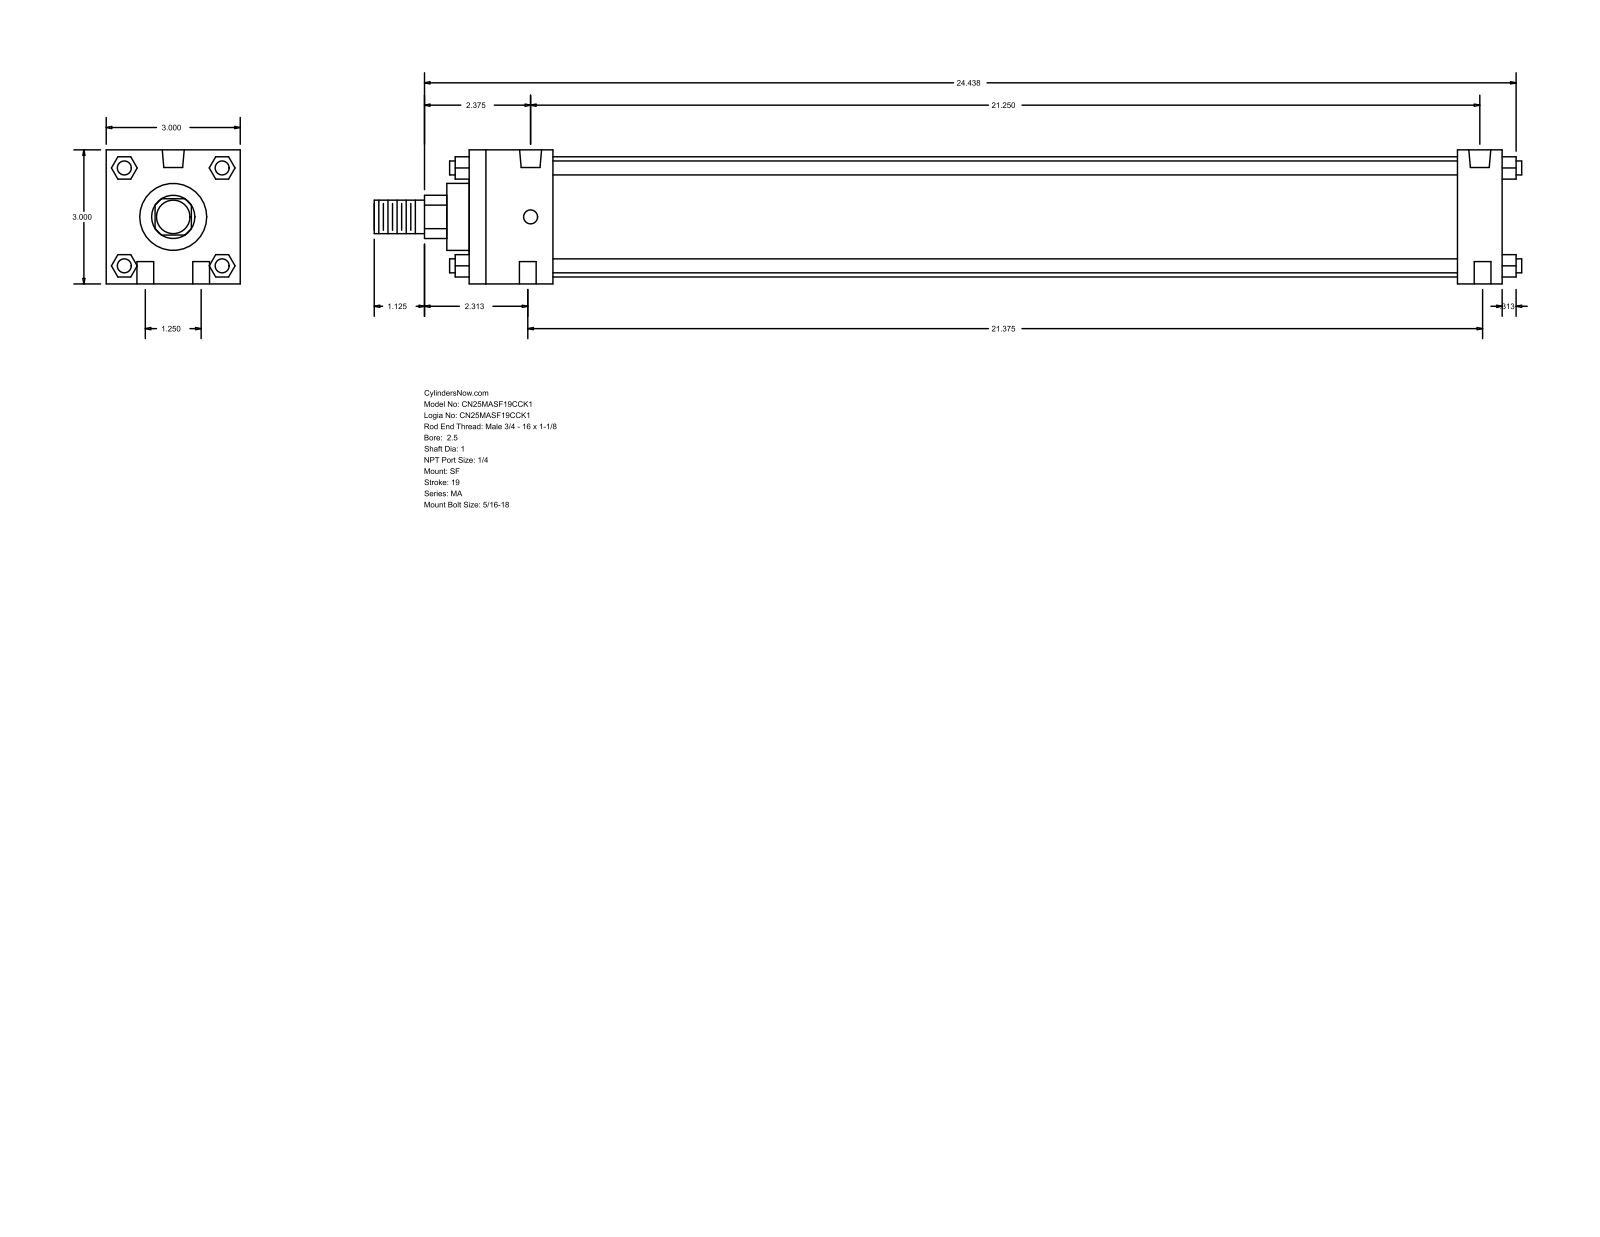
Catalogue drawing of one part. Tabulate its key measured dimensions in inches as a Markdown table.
| quantity | value |
| --- | --- |
| part name | MA_SF__0250_1 |
| STEP written by | GSSL Pune (CONFIG_CONTROL_DESIGN) |
| units | inches |
| bodies | 0 solids, 124 faces (94 planar, 30 cylindrical, 0 other) |
| overall size | 25.687 × 3 × 3 |
| round holes (diameter × count) | 0.375 × 4, 0.313 × 2, 0.492 × 2 |
| round bosses / shafts (diameter × count) | 0.313 × 4, 2.69 × 1, 1.5 × 1, 1 × 1, 0.75 × 1 |
| partial cylindrical surfaces (radius × count) | 0.484 × 1 |
| main face-to-face distances | 3, 23.125, 0.5, 22.125, 1, 1.875, 20.25, 21.25, 1.095, 1.896 |
| hole center spacings | 0.628, 1.25, 21.25, 21.321, 21.322, 21.375, 21.411 |
